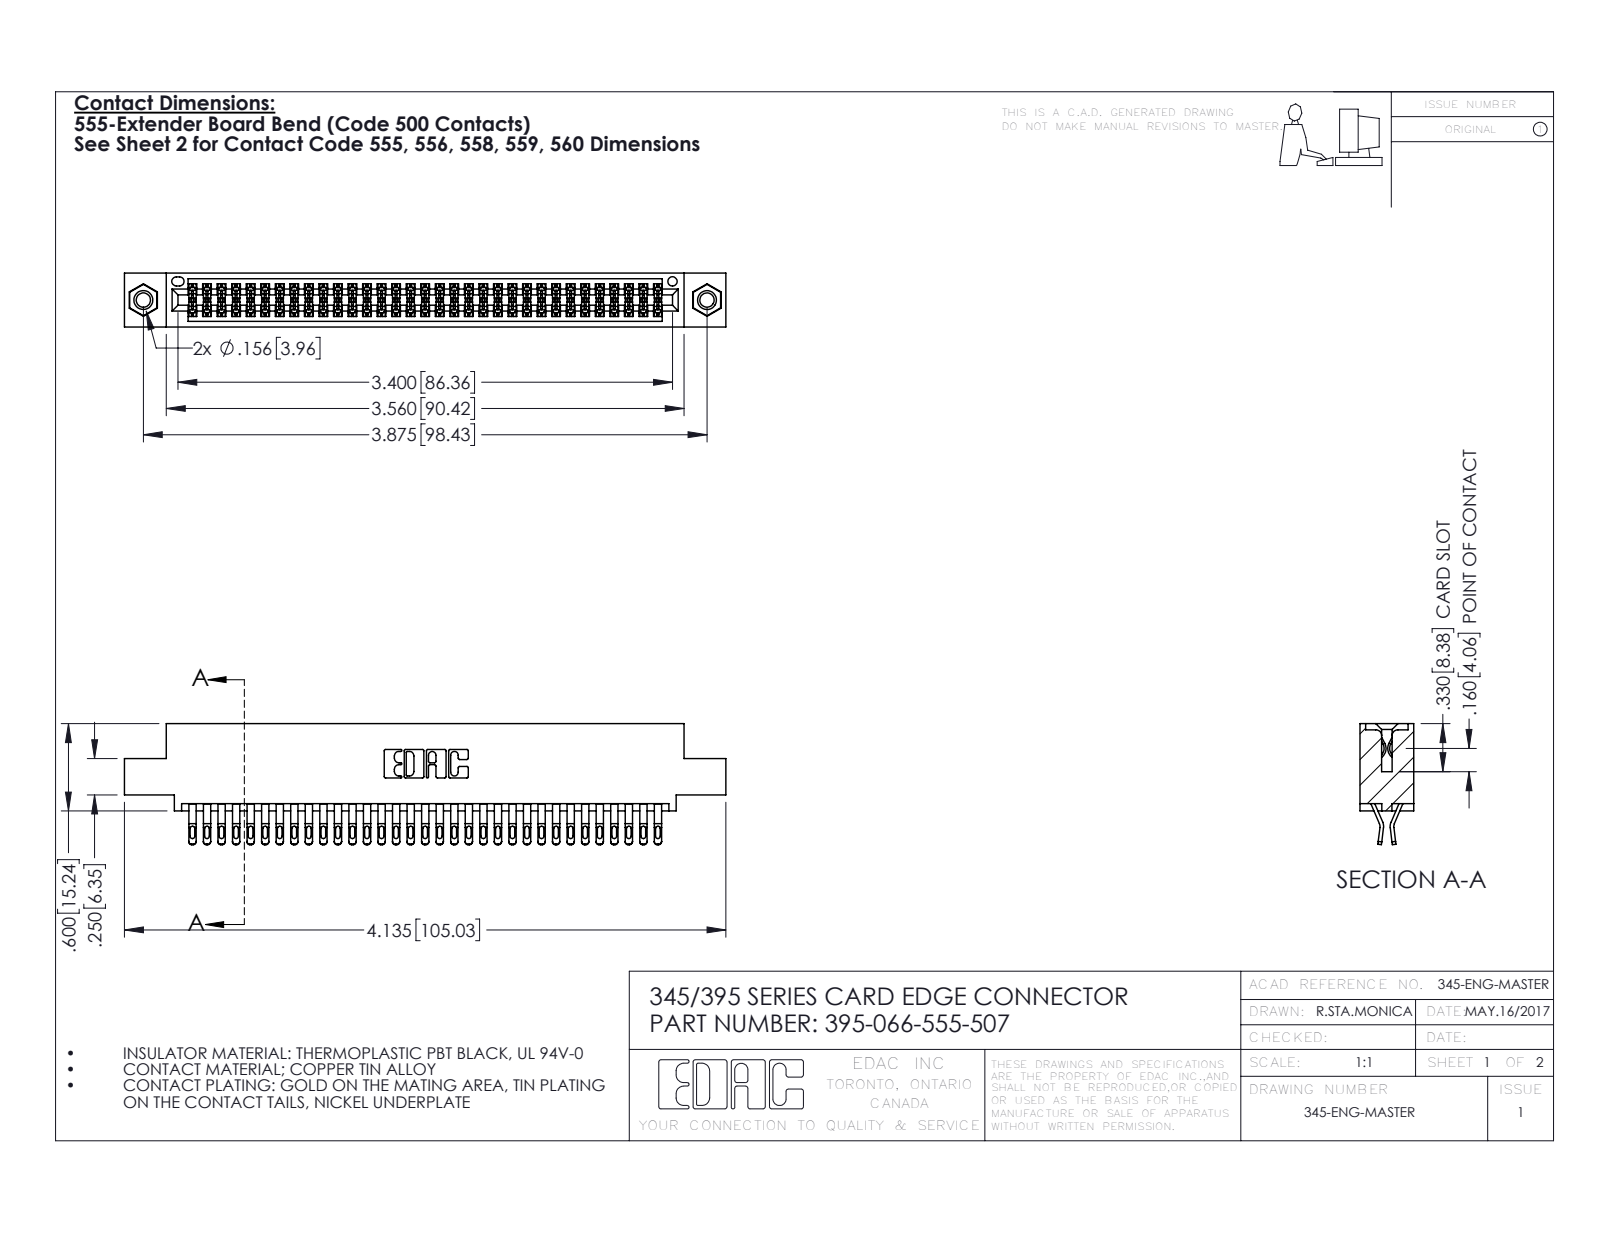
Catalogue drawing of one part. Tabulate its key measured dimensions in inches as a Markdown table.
| quantity | value |
| --- | --- |
| part name | 345-292-001_555 Tail; 395-066-555-507; 345-250-001_345-250-005-103; 345 Part_0.110 Offset - 0.156 Dia-TI |
| STEP written by | SolidWorks 2016 (CONFIG_CONTROL_DESIGN) |
| units | inches |
| bodies | 69 solids, 3886 faces (2162 planar, 1708 cylindrical, 16 other) |
| overall size | 4.135 × 0.832 × 0.37 |
| volume | 0.624 in³ |
| surface area | 24.37 in² |
| round holes (diameter × count) | 0.098 × 2, 0.125 × 2, 0.156 × 2, 0.064 × 1 |
| round bosses / shafts (diameter × count) | 0.155 × 2 |
| partial cylindrical surfaces (radius × count) | 0.016 × 165, 0.02 × 132, 0.006 × 99, 0.01 × 22, 0.007 × 6, 0.031 × 6, 0.026 × 3, 0.01 × 2 |
| main face-to-face distances | 0.072, 0.298, 0.2, 0.37, 0.025, 0.098, 0.272, 0.225, 0.175, 0.149 |
| hole center spacings | 0.27, 3.64, 3.875 |
